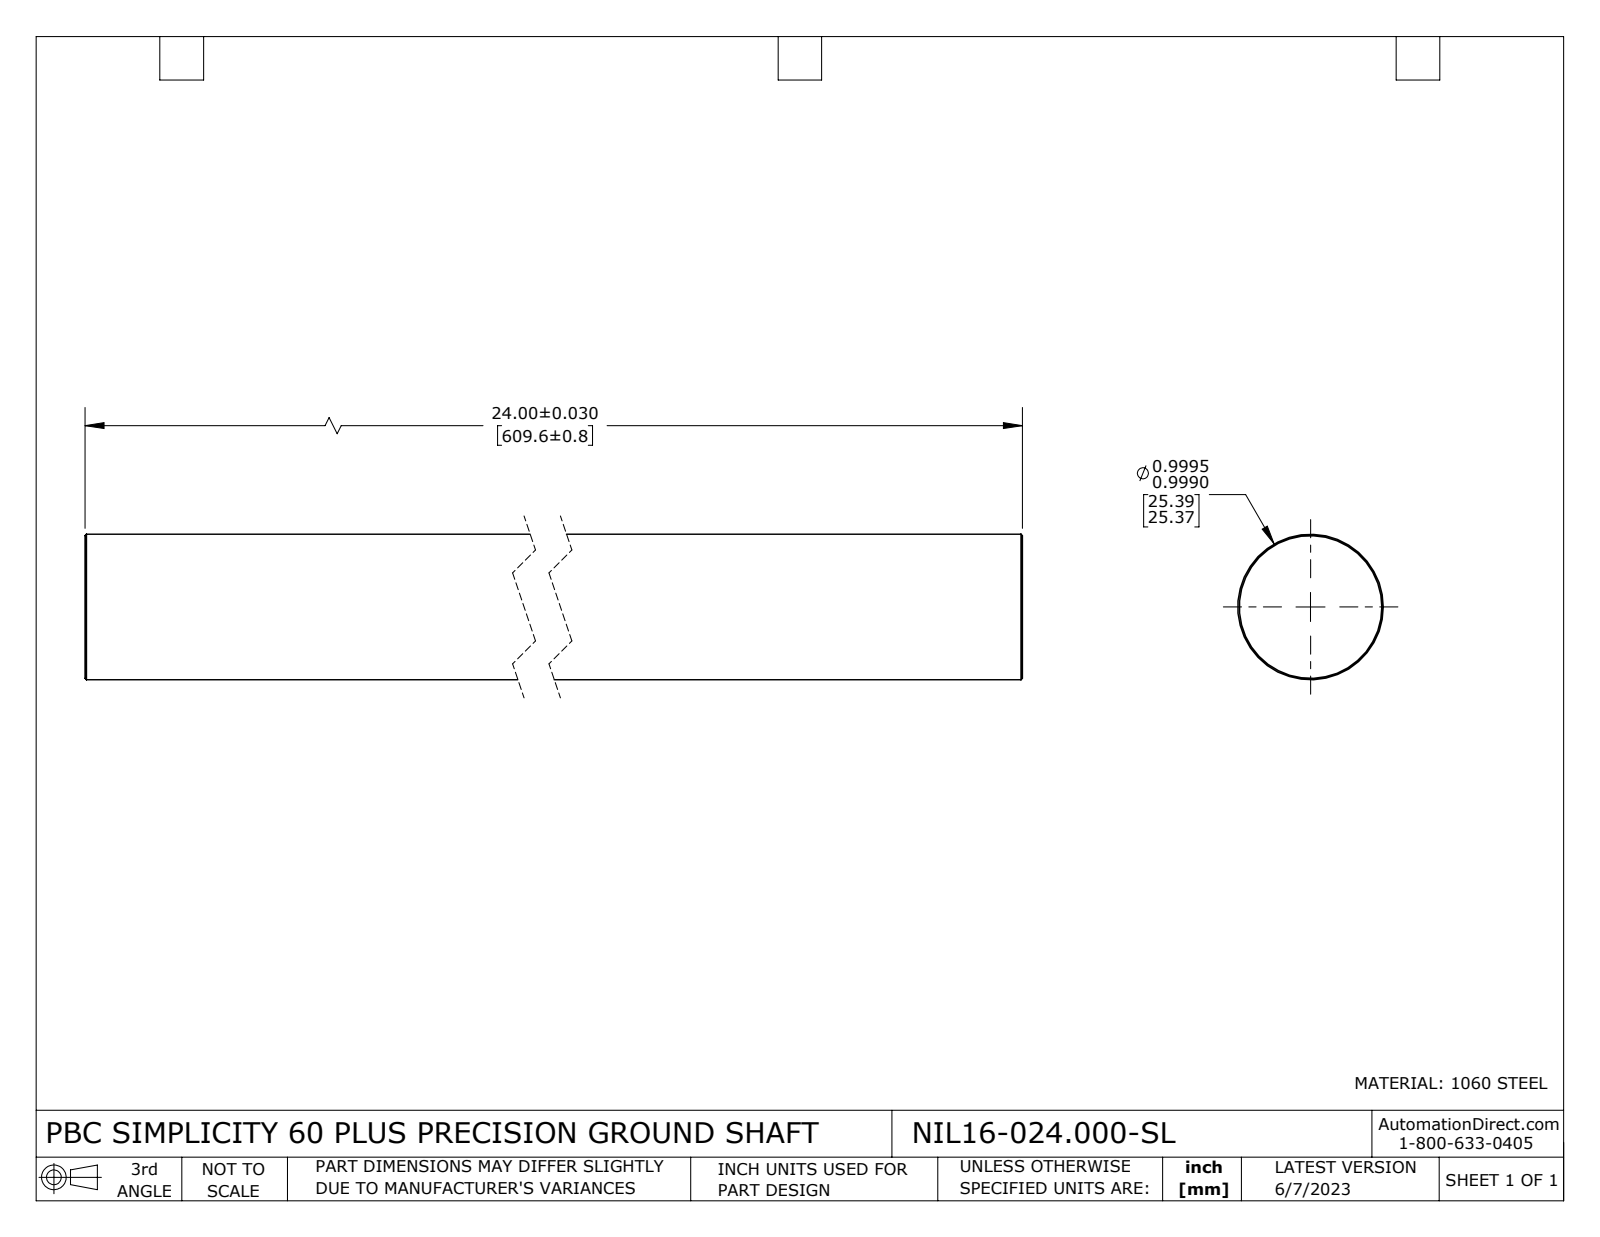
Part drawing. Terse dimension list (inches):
name: NIL16-024.000-SL
written by: SolidWorks 2021 (CONFIG_CONTROL_DESIGN)
unit: in
bodies: 1 solid, 8 faces (2 planar, 2 cylindrical, 4 other)
size: 24 × 1 × 1
volume: 18.85 in³; area: 76.93 in²
bosses: 1× ⌀1
face distances: 24
